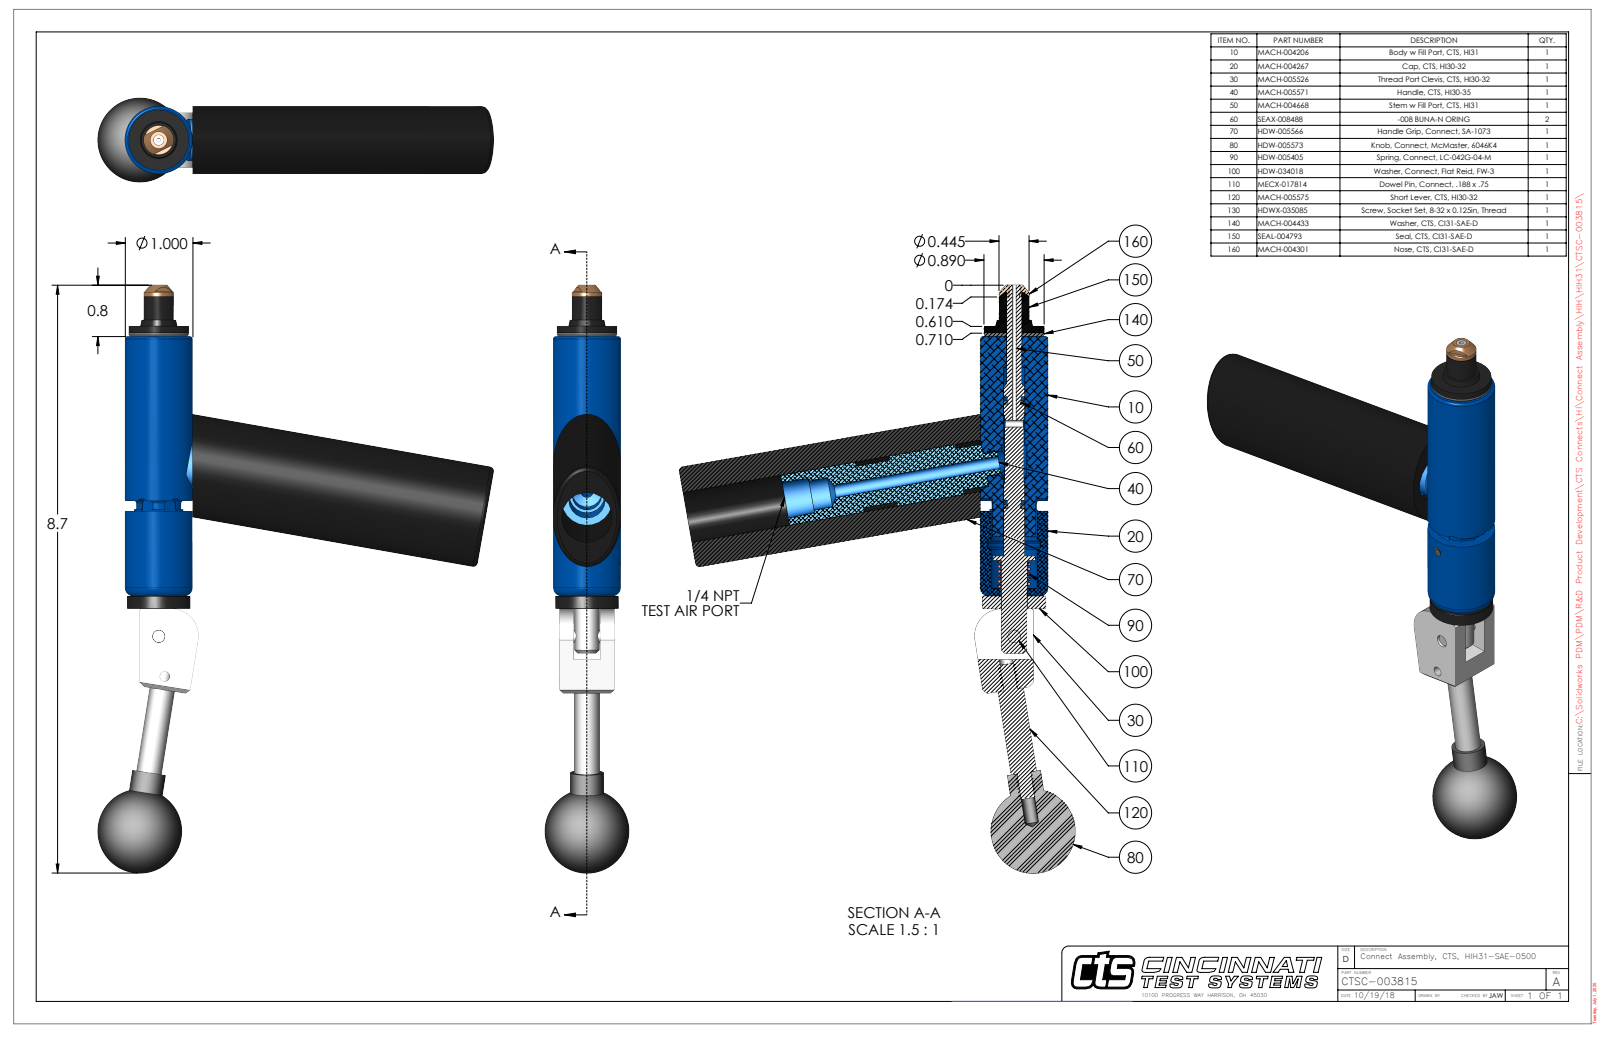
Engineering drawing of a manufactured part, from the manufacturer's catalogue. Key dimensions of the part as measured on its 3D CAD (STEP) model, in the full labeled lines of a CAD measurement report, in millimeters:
Part name (STEP PRODUCT): CTSC-003815
STEP written by: SolidWorks 2023 (AUTOMOTIVE_DESIGN)
Units: millimetres
Bodies: 10 solids, 321 faces (118 planar, 128 cylindrical, 75 other)
Overall size (bounding box): 220.8 × 148.7 × 31.8
Volume: 152 900 mm³ · Surface area: 49 500 mm²
Round holes (diameter × count): ⌀3.8 ×2, ⌀5.1 ×2, ⌀1.6 ×1, ⌀2.8 ×1, ⌀3.5 ×1, ⌀4.7 ×1, ⌀4.8 ×1, ⌀5.8 ×1, ⌀5.8 ×1, ⌀9.8 ×1, ⌀10 ×1, ⌀11.1 ×1
Round bosses / shafts (diameter × count): ⌀25.4 ×1, ⌀23.8 ×1, ⌀22.6 ×1, ⌀19.1 ×1, ⌀15.7 ×1, ⌀12.7 ×1, ⌀11.3 ×1, ⌀11.3 ×1
Partial cylindrical surfaces — rounded edges, fillets, slot ends (radius × count): R2.4 ×6, R0.7 ×2, R1.6 ×1, R8.3 ×1, R9.5 ×1, R10.2 ×1, R11.6 ×1
Main face-to-face distances: 5.3, 15.3, 1.3, 98.7, 97.4, 20.6, 103.4, 102.2, 4.7, 9.9
Hole centre spacings: 15.2, 42.1, 57.2
